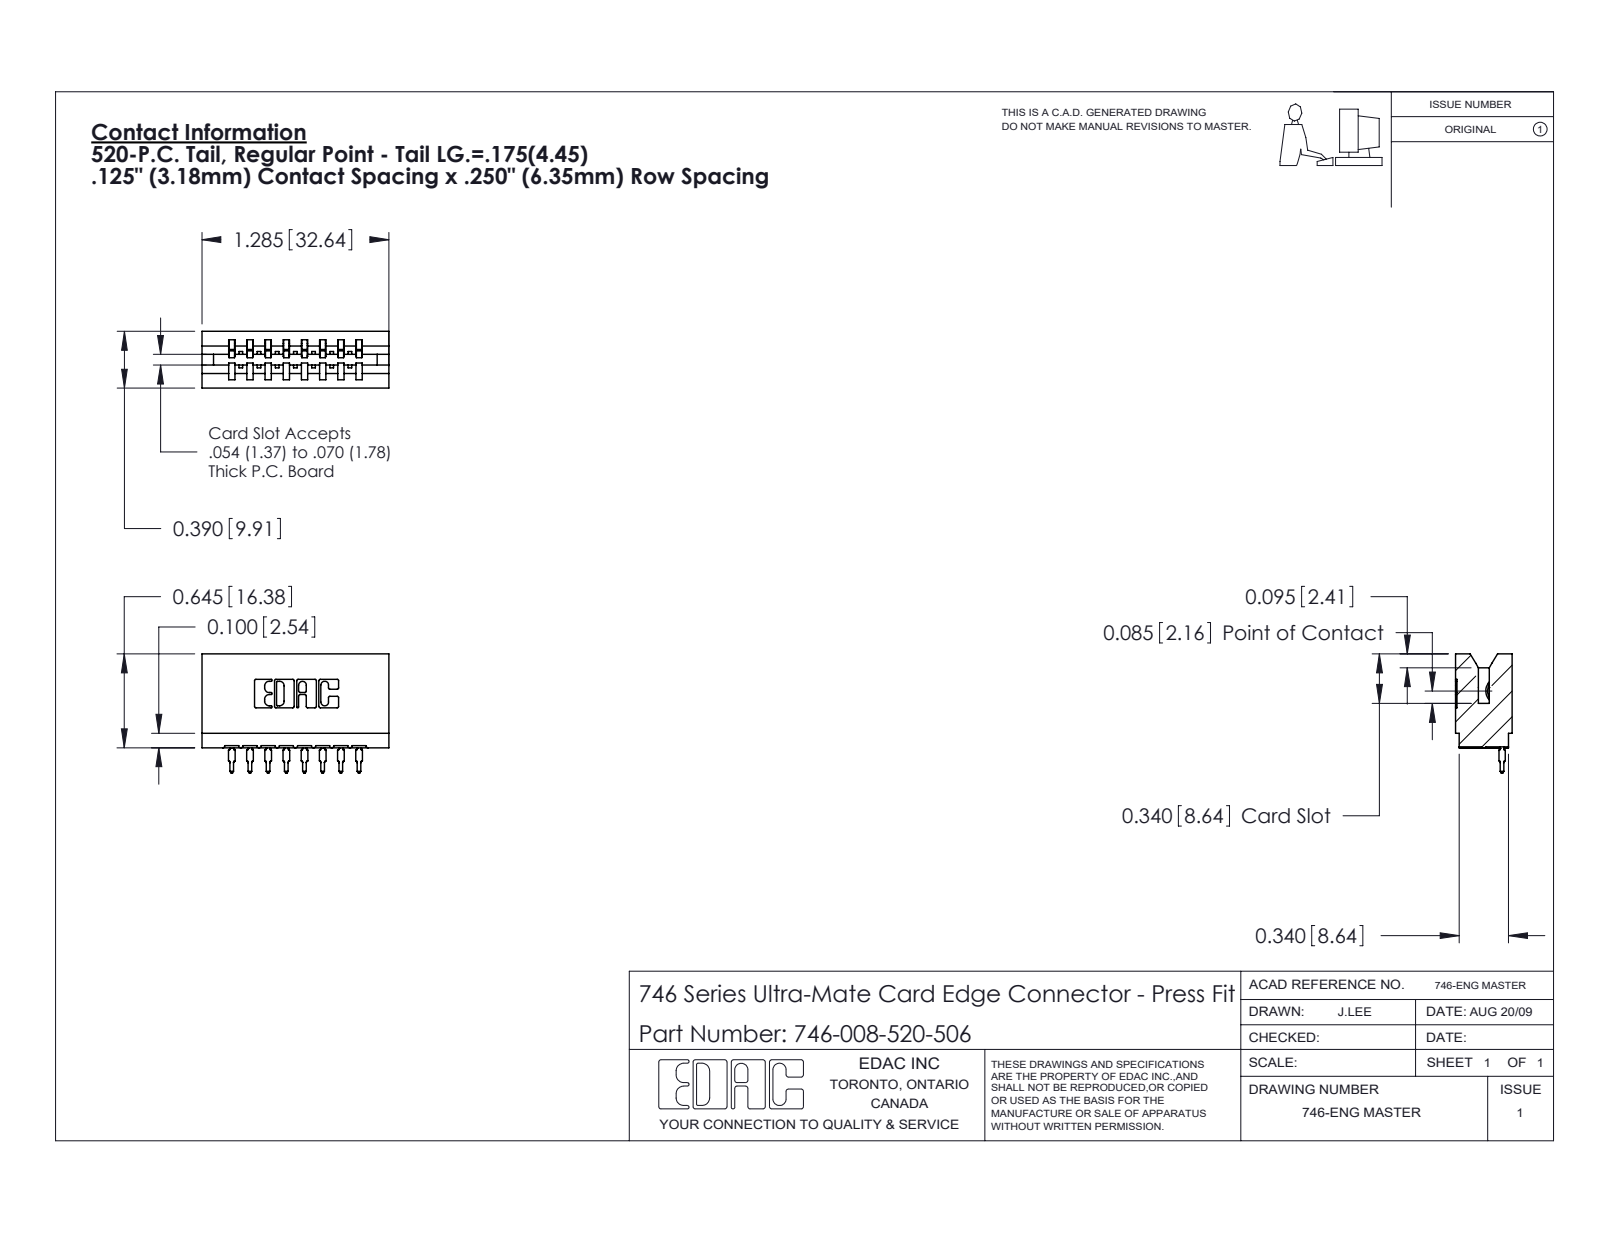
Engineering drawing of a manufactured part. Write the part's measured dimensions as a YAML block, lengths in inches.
part_name: "746-008-520-506; 746-292-001_520; 746 Part_.340 Slot Depth - 06"
step_written_by: "SolidWorks 2020 (CONFIG_CONTROL_DESIGN)"
units: inches
bodies: {solids: 9, faces: 962, planar: 560, cylindrical: 194, other: 208}
overall_size: [1.285, 0.819, 0.39]
volume: 0.234
surface_area: 7.144
partial_cylinders:
  - {radius: 0.01, count: 22}
  - {radius: 0.021, count: 16}
  - {radius: 0.015, count: 9}
  - {radius: 0.007, count: 6}
  - {radius: 0.031, count: 6}
  - {radius: 0.005, count: 4}
  - {radius: 0.011, count: 4}
  - {radius: 0.026, count: 3}
face_to_face_distances: [0.25, 0.042, 0.125, 0.5, 0.333, 0.292, 0.375, 0.208, 0.125, 0.057]
